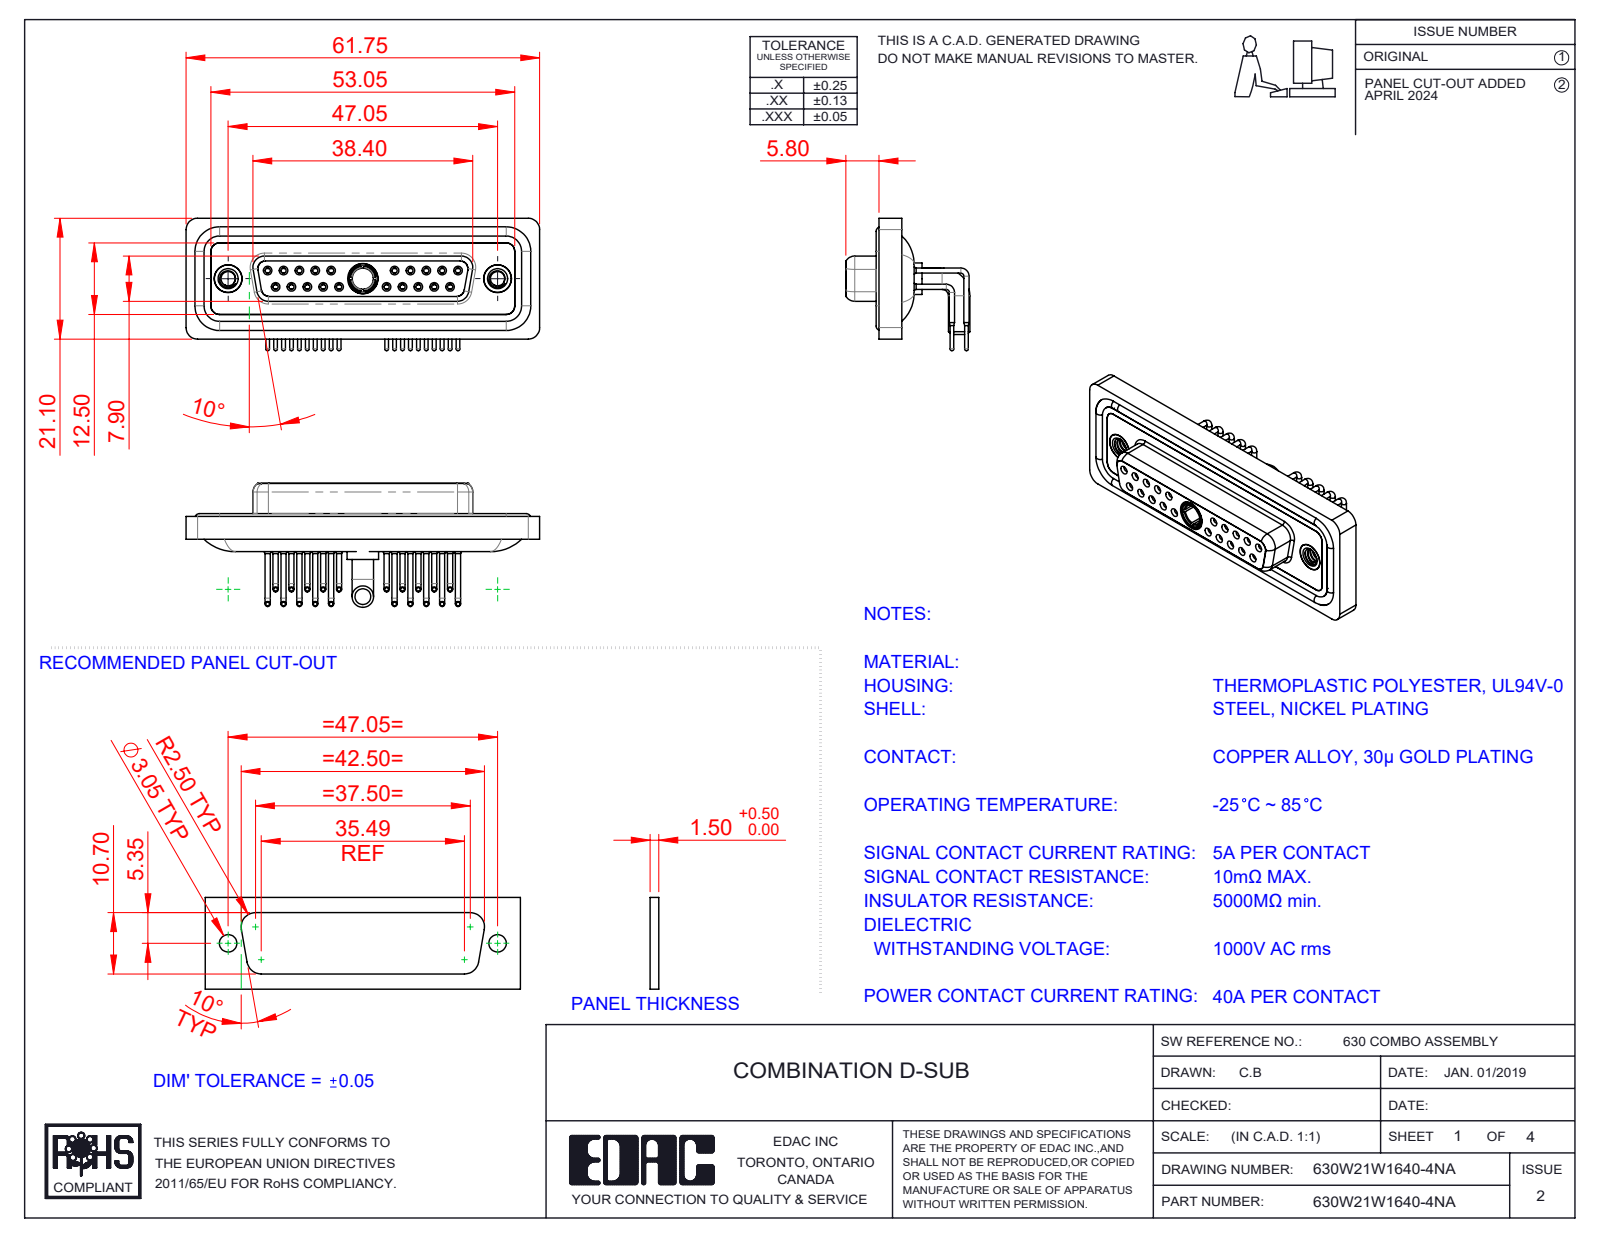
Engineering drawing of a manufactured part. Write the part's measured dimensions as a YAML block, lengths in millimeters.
part_name: "630Combo Housing_21W1; 630Combo Threaded Rivet_A; 630Combo Shell Front_25 Contacts; 630W21W1640-4NA (+5 more)"
step_written_by: "SolidWorks 2023 (CONFIG_CONTROL_DESIGN)"
units: millimeters
bodies: {solids: 29, faces: 1518, planar: 434, cylindrical: 671, other: 413}
overall_size: [61.75, 23.12, 21.68]
volume: 8571
surface_area: 14827
round_holes:
  - {diameter: 0.9, count: 20}
  - {diameter: 1.1, count: 20}
  - {diameter: 1.5, count: 20}
  - {diameter: 2, count: 20}
  - {diameter: 1.6, count: 10}
  - {diameter: 1.7, count: 10}
  - {diameter: 4.85, count: 3}
  - {diameter: 2.5, count: 2}
  - {diameter: 4, count: 2}
  - {diameter: 4.05, count: 2}
  - {diameter: 5, count: 2}
  - {diameter: 3.7, count: 1}
round_bosses_or_shafts:
  - {diameter: 0.9, count: 20}
  - {diameter: 0.65, count: 20}
  - {diameter: 1.6, count: 14}
  - {diameter: 4.95, count: 2}
  - {diameter: 4.8, count: 2}
  - {diameter: 3.75, count: 2}
  - {diameter: 5.5, count: 1}
  - {diameter: 5.2, count: 1}
partial_cylinders:
  - {radius: 1.5, count: 18}
  - {radius: 2, count: 18}
  - {radius: 1.35, count: 8}
  - {radius: 1.6, count: 8}
  - {radius: 0.25, count: 4}
  - {radius: 0.5, count: 4}
  - {radius: 0.6, count: 4}
  - {radius: 0.65, count: 4}
face_to_face_distances: [0.4, 1.8, 4.1, 1.6, 1.1, 2.5, 3.1, 1.5, 9.8, 0.45]
hole_center_spacings: [3.16, 2.77, 5.54, 8.31, 5.04, 19.39, 20.97, 22.16]
